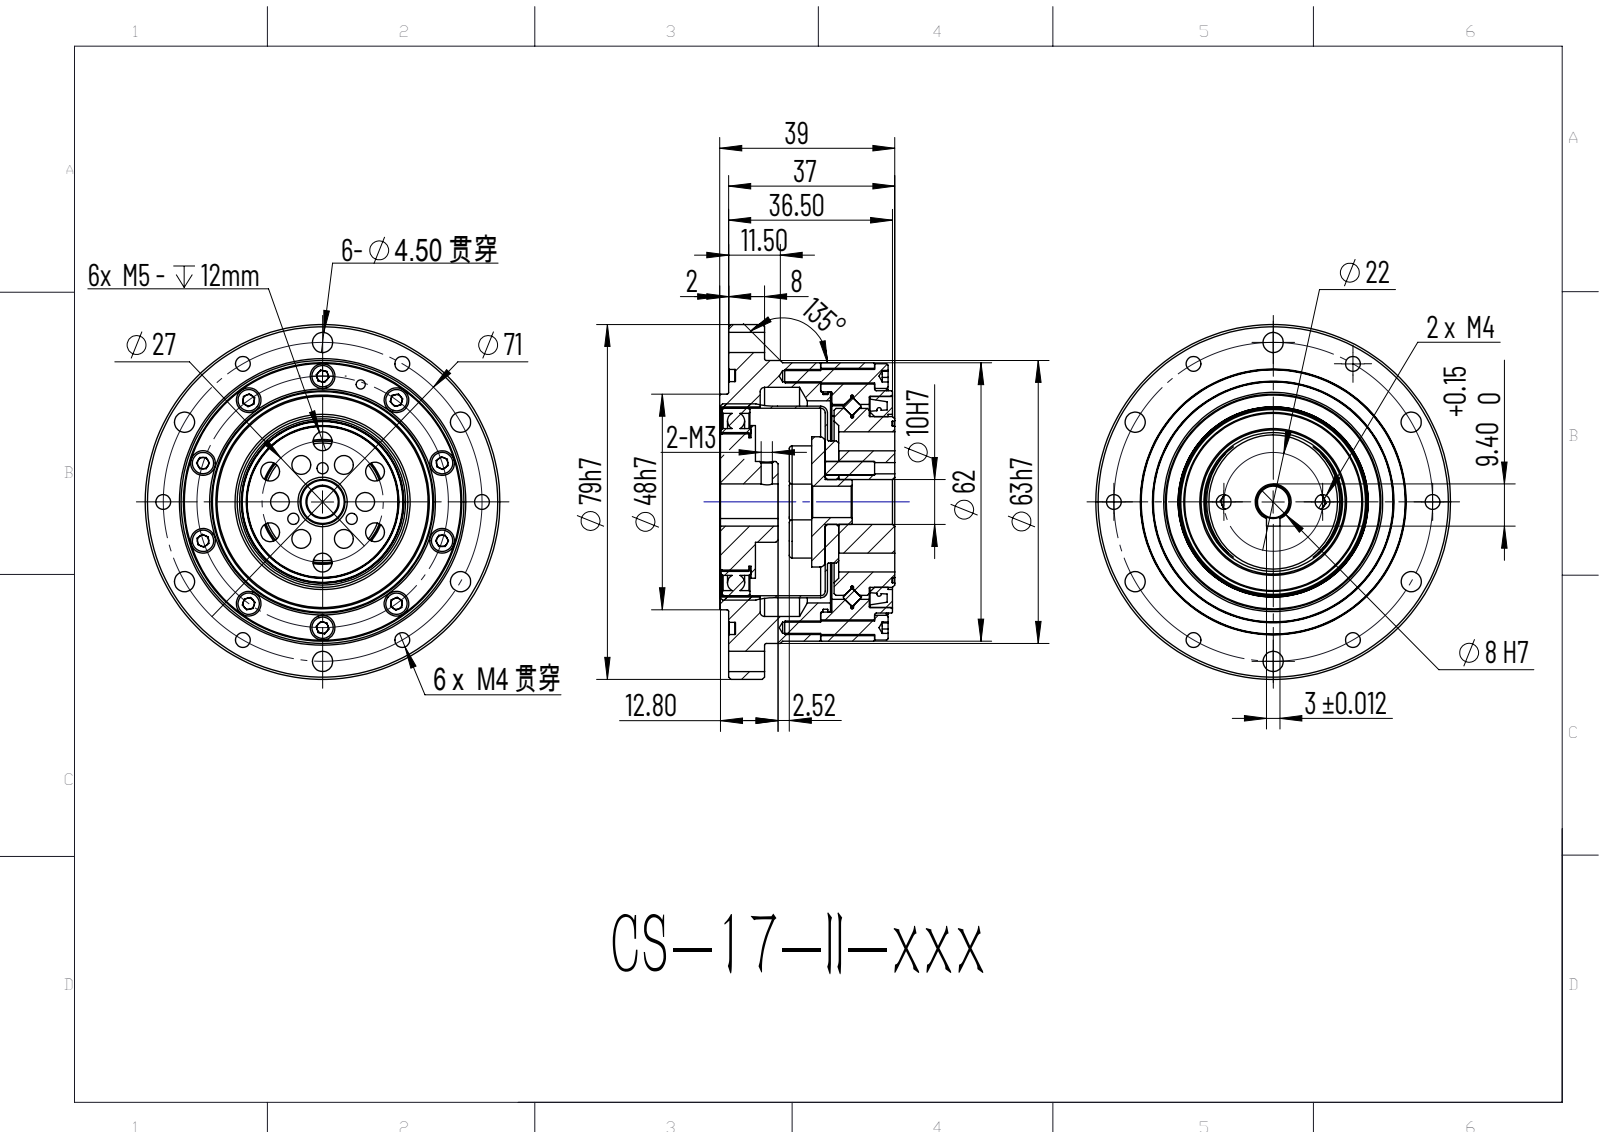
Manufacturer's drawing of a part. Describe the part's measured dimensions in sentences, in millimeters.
The part is named "CS-17-II; hexagon socket head cap screws gb_GB_FASTENER_SCREWS_HSHCS M3X20-C; 17??????; 17-?? (+8 more)". Its 3-D file was written by "ONSHAPE BY PTC INC, 1.201 (AP242_MANAGED_MODEL_BASED_3D_ENGINEERING_MIM_LF)". It is 73 solids with 857 faces: 411 planar, 204 cylindrical and 242 other. Overall it measures 79 by 79 by 39 millimeters. Its volume is 91 649 cubic millimeters and its surface area 65 240 square millimeters. Round holes: 15 of diameter 2.5, 12 of diameter 4.2, 10 of diameter 3.5, 8 of diameter 3.3, 6 of diameter 4.5, 6 of diameter 5.5, 3 of diameter 3, 1 of diameter 2.05, 1 of diameter 2.9, 1 of diameter 5, 1 of diameter 7, 1 of diameter 8. Round bosses or shafts: 54 of diameter 3, 10 of diameter 5.5, 6 of diameter 8.5, 6 of diameter 5, 1 of diameter 79, 1 of diameter 63, 1 of diameter 62, 1 of diameter 53.6. The main face-to-face distances are 1, 20.5, 13.5, 8, 15, 1.5, 12.5, 24.5, 3, 16.5. The hole center spacings are 35.5, 9.5, 27.68, 31.83, 41.08, 50.2, 68.58, 28.
